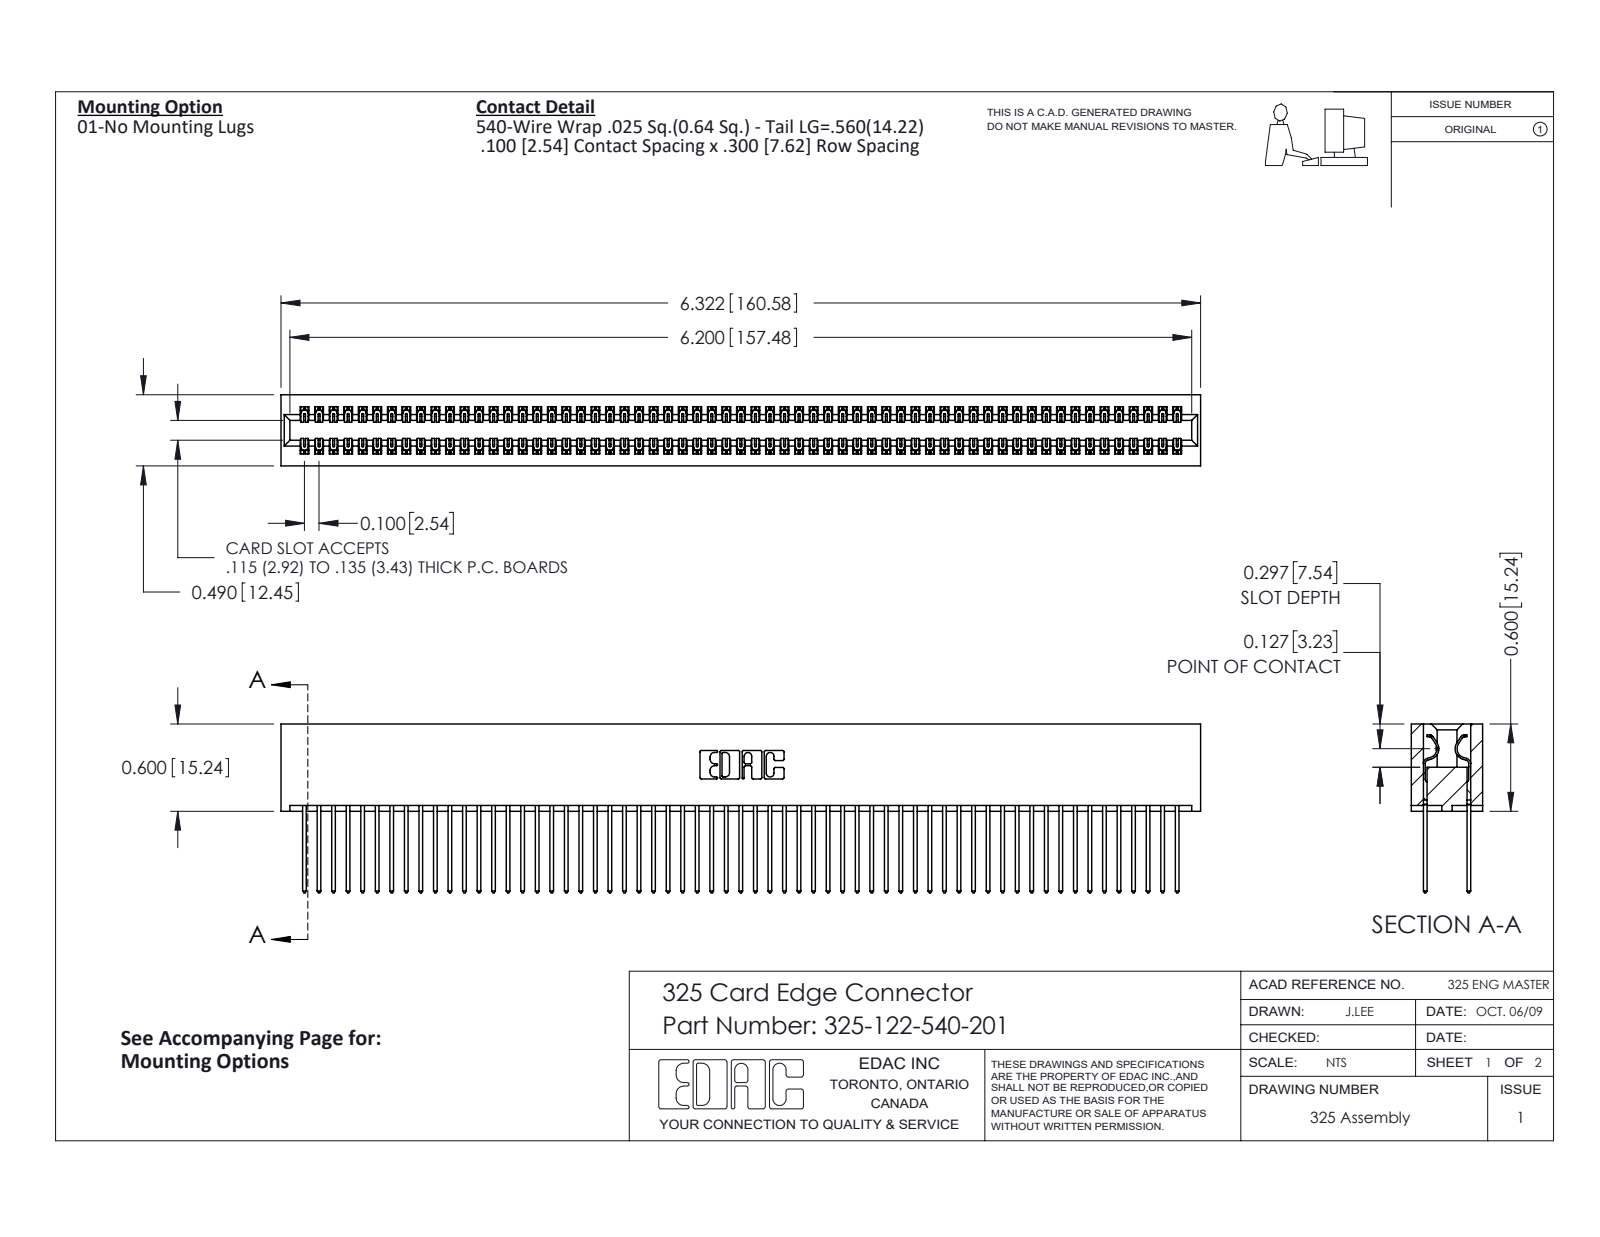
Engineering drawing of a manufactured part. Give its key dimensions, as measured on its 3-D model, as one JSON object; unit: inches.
{"part_name": "325 Part_Lugless; 325-292-001_325-293-140; 325-122-540-201", "step_written_by": "SolidWorks 2016 (CONFIG_CONTROL_DESIGN)", "units": "inches", "bodies": {"solids": 123, "faces": 6450, "planar": 4458, "cylindrical": 1992, "other": 0}, "overall_size": [6.322, 1.16, 0.49], "volume_in3": 1.341, "surface_area_in2": 46.35, "partial_cylinders_radius": [[0.006, 183], [0.01, 122], [0.01, 22], [0.007, 6], [0.031, 6], [0.026, 3], [0.014, 2], [0.022, 2]], "face_to_face_distances": [0.083, 0.407, 0.3, 0.107, 0.383, 0.025, 0.325, 0.49, 0.275, 0.56]}
